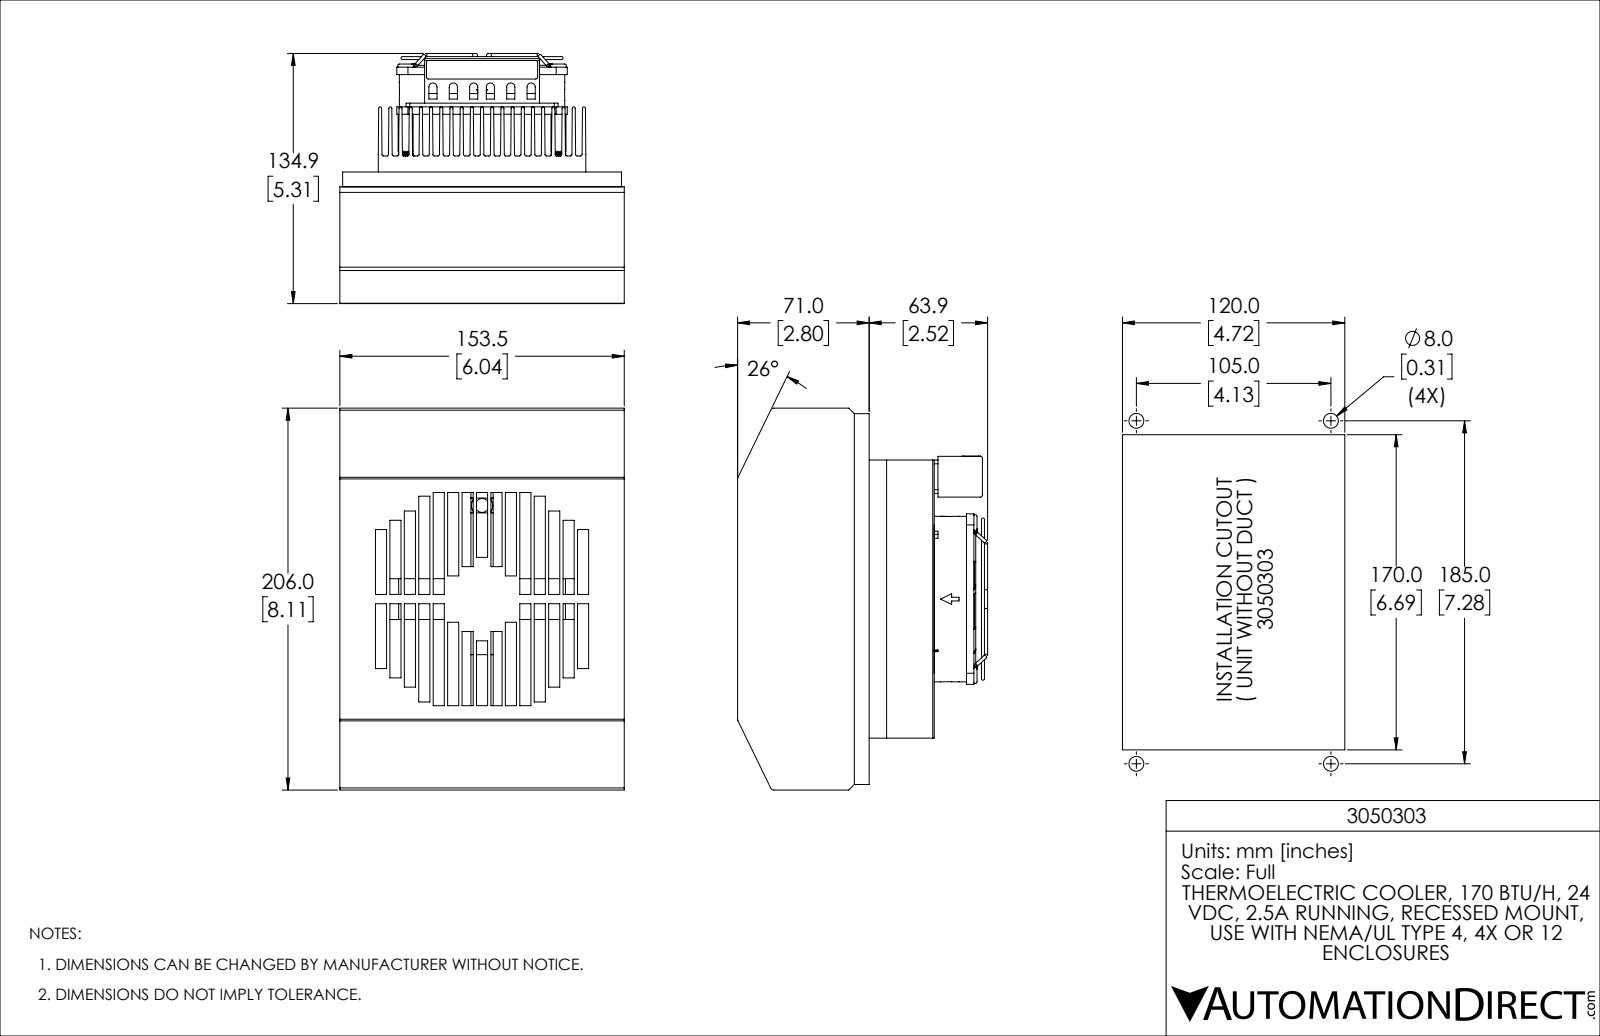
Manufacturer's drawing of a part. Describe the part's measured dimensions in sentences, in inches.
The part is named "3050303". Its 3-D file was written by "SolidWorks 2019 (AUTOMOTIVE_DESIGN)". It is 18 solids with 1526 faces: 596 planar, 853 cylindrical and 77 other. Overall it measures 8.11 by 6.043 by 5.312 inches. Its volume is 38.85 cubic inches and its surface area 618.3 square inches. Round holes: 12 of diameter 0.165, 9 of diameter 0.236, 9 of diameter 0.504, 7 of diameter 0.098, 5 of diameter 0.315, 4 of diameter 0.126, 4 of diameter 0.13, 4 of diameter 0.169, 4 of diameter 0.244, 2 of diameter 0.138, 1 of diameter 0.295, 1 of diameter 3.393. Round bosses or shafts: 12 of diameter 0.071, 4 of diameter 0.153, 4 of diameter 0.114, 3 of diameter 0.157, 1 of diameter 3.515, 1 of diameter 1.887. Partial cylindrical surfaces (rounded edges, fillets, slot ends): 96 of radius 0.054, 61 of radius 0.031, 48 of radius 0.005, 17 of radius 0.039, 8 of radius 0.079, 6 of radius 0.087, 4 of radius 0.157, 4 of radius 0.236. The main face-to-face distances are 0.217, 0.65, 0.433, 0.866, 1.083, 1.299, 1.516, 1.732, 0.039, 1.949. The hole center spacings are 0.278, 0.289, 0.447, 0.568, 0.686, 1.22, 0.35, 1.27.
